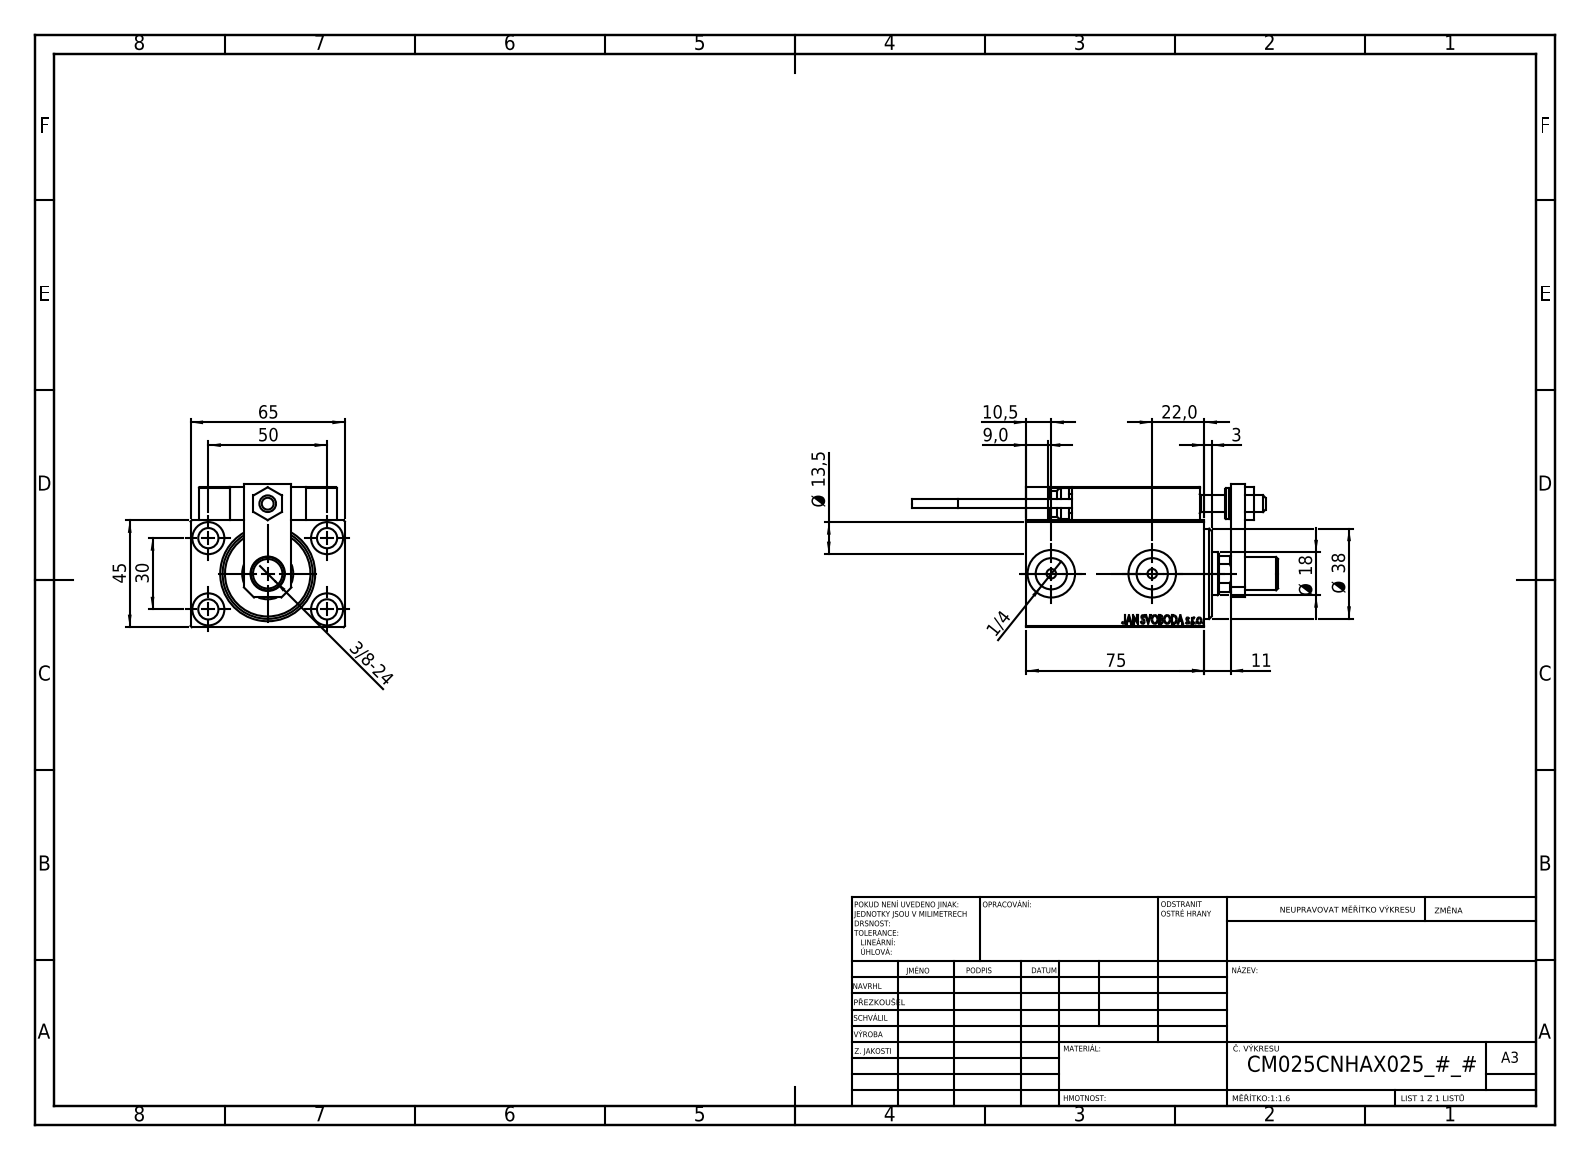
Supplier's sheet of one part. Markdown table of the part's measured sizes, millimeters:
| quantity | value |
| --- | --- |
| part name | SWITCH DIM B,W; TYC_L79; NUT_D12; ZARAZKA (+7 more) |
| STEP written by | SolidWorks 2019 (CONFIG_CONTROL_DESIGN) |
| units | millimeters |
| bodies | 24 solids, 1295 faces (563 planar, 192 cylindrical, 540 other) |
| overall size | 154 × 65 × 60.5 |
| volume | 238 637 mm³ |
| surface area | 72 791 mm² |
| round holes (diameter × count) | 4 × 6, 8 × 5, 8.5 × 5, 3.2 × 4, 13.5 × 4, 5 × 2, 13.16 × 2, 20 × 2, 7 × 1, 14.5 × 1, 18 × 1, 21.5 × 1 |
| round bosses / shafts (diameter × count) | 5 × 2, 3.8 × 2, 14 × 1, 13 × 1, 12 × 1, 11 × 1 |
| partial cylindrical surfaces (radius × count) | 0.3 × 30, 3 × 2, 8.5 × 1 |
| main face-to-face distances | 45, 14, 65, 6, 59, 13, 3, 19, 3.5, 20 |
| hole center spacings | 29.15, 11.37, 20, 27.07, 28.9, 29.59, 29.69, 30 |
